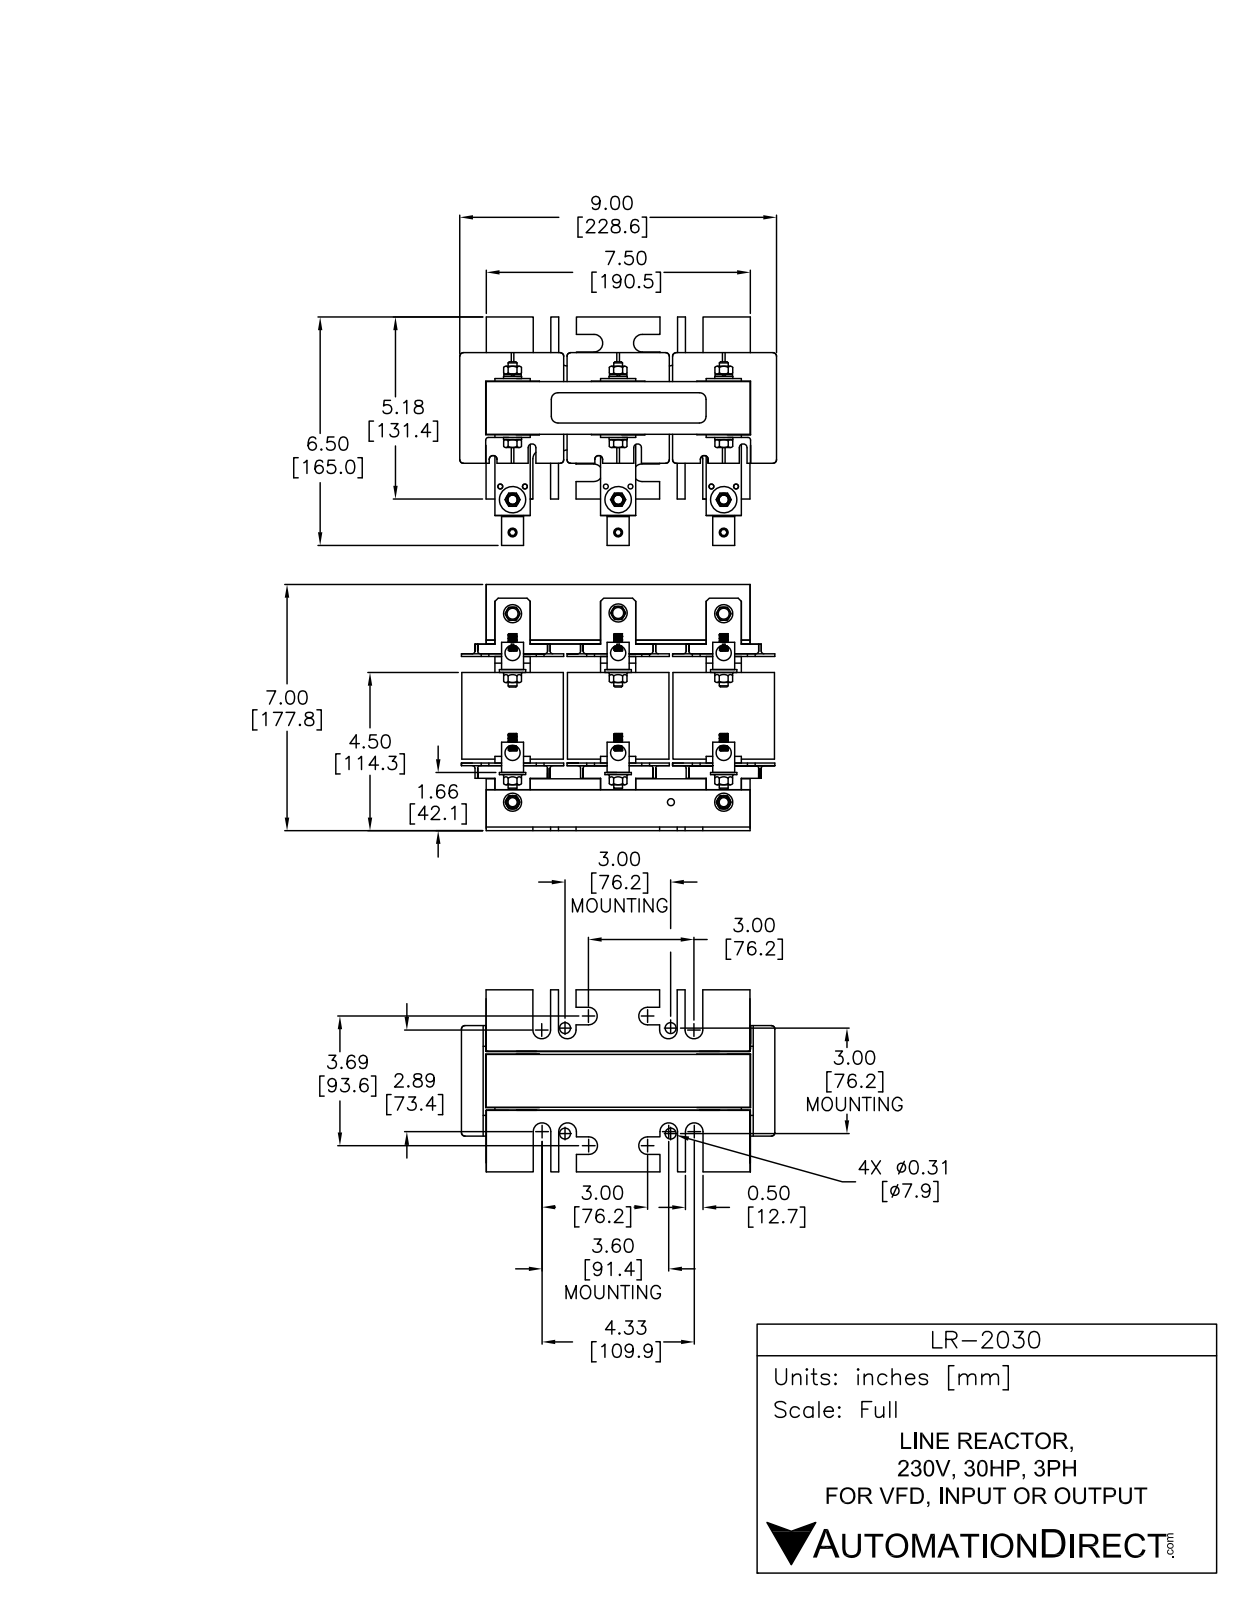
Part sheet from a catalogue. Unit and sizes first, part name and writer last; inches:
Units: inches
Overall size (bounding box): 8.937 × 6.996 × 6.329
Round holes (diameter × count): ⌀0.423 ×6, ⌀0.453 ×3, ⌀0.453 ×3
Round bosses / shafts (diameter × count): ⌀0.591 ×11, ⌀0.738 ×9, ⌀0.236 ×9, ⌀0.413 ×6, ⌀0.236 ×2
Partial cylindrical surfaces — rounded edges, fillets, slot ends (radius × count): R0.591 ×16, R0.25 ×12, R0.276 ×12, R0.108 ×6, R0.6 ×6, R0.059 ×4, R0.923 ×3, R0.945 ×3
Main face-to-face distances: 3.012, 0.079, 0.354, 3.445, 3.366, 0.276, 3.091, 1.496, 1.516, 1.673
Hole centre spacings: 3.012, 3.025, 4.122, 6.024, 0.282, 2.815, 6.03, 6.649
Volume: 162.8 in³ · Surface area: 860.3 in²
Bodies: 47 solids, 972 faces (716 planar, 244 cylindrical, 12 other)
Part name (STEP PRODUCT): LR-2030
STEP written by: SolidWorks 2011 (AUTOMOTIVE_DESIGN)
